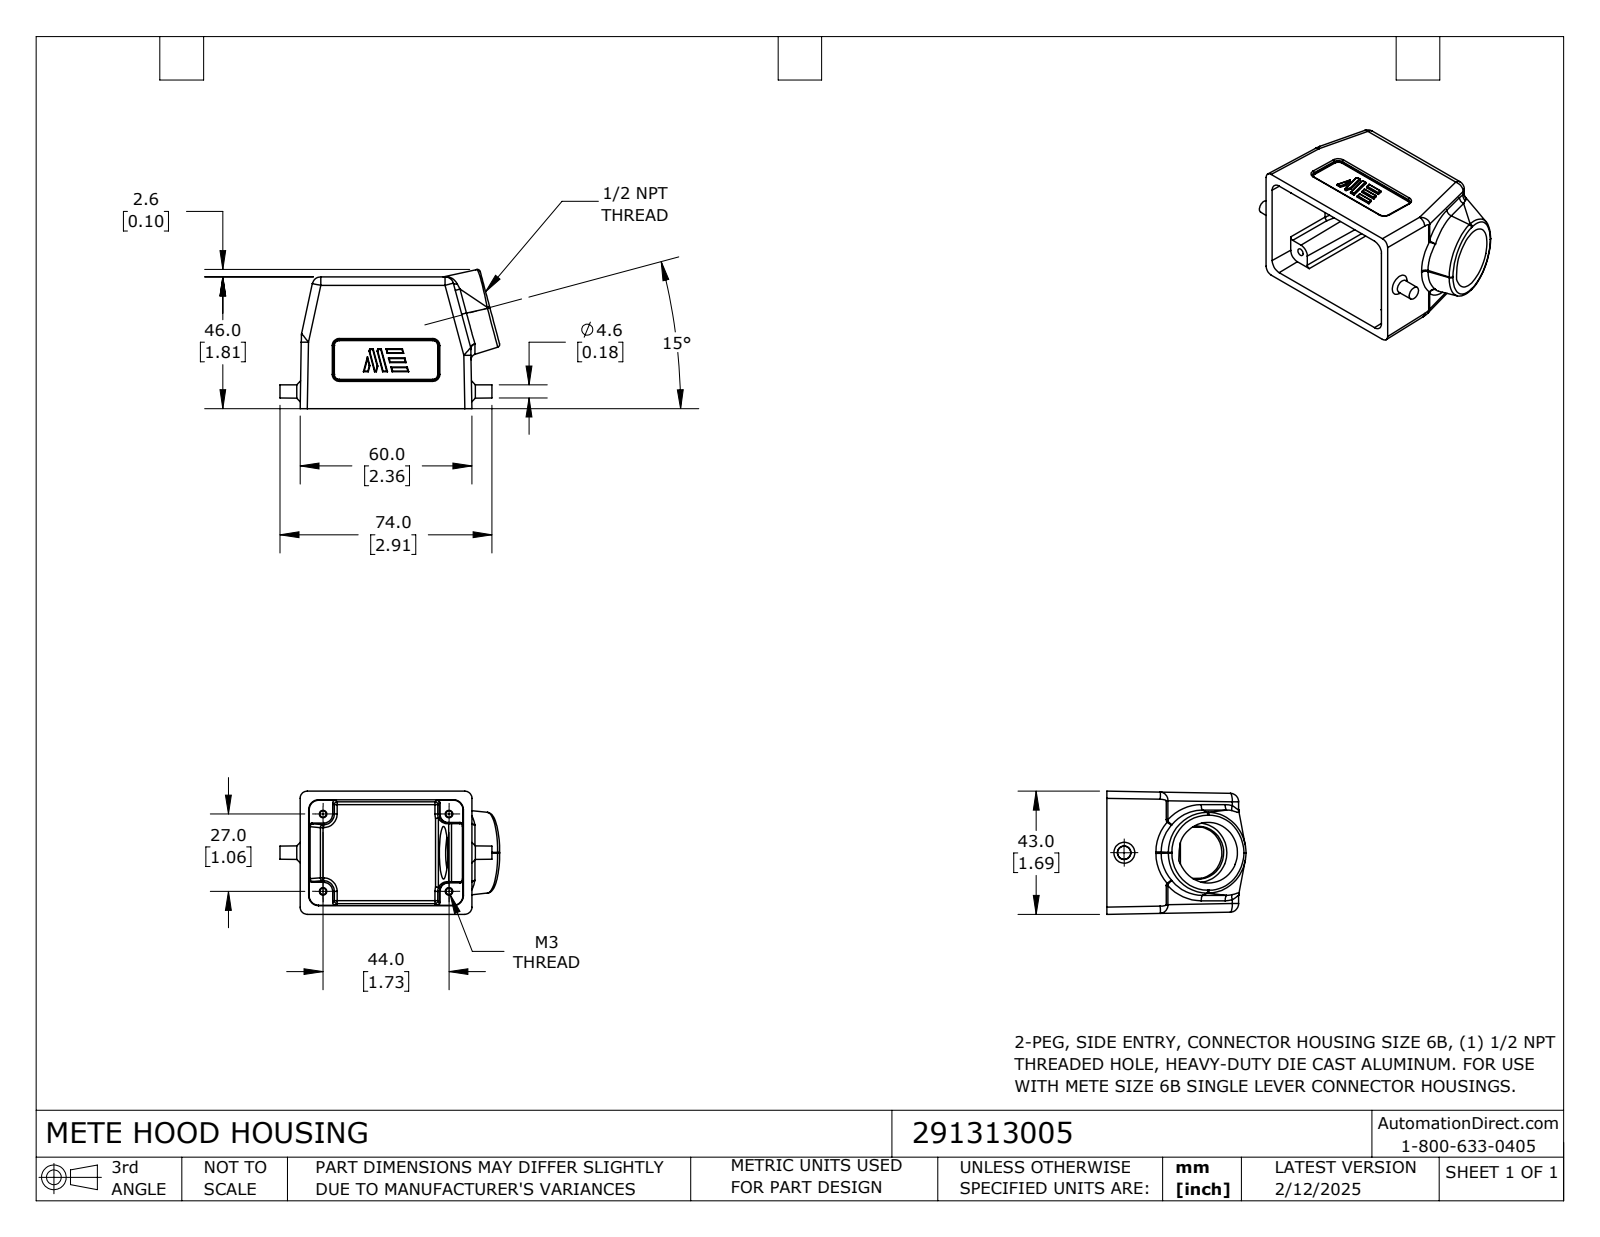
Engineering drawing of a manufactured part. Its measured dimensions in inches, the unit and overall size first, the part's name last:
Units: inches
Overall size (bounding box): 3.019 × 1.913 × 1.693
Round holes (diameter × count): ⌀0.102 ×4
Partial cylindrical surfaces — rounded edges, fillets, slot ends (radius × count): R0.008 ×47, R0.039 ×22, R0.02 ×8, R0.079 ×8, R0.118 ×8, R0.098 ×6, R0.075 ×4
Main face-to-face distances: 0.118, 0.041, 0.077, 1.693, 1.811, 0.323, 0.441, 0.315, 0.433, 0.392
Hole centre spacings: 1.063, 1.732, 2.032
Volume: 2.409 in³ · Surface area: 34.32 in²
Bodies: 1 solid, 341 faces (117 planar, 134 cylindrical, 90 other)
Part name (STEP PRODUCT): 291313005
STEP written by: SolidWorks 2024 (CONFIG_CONTROL_DESIGN)
